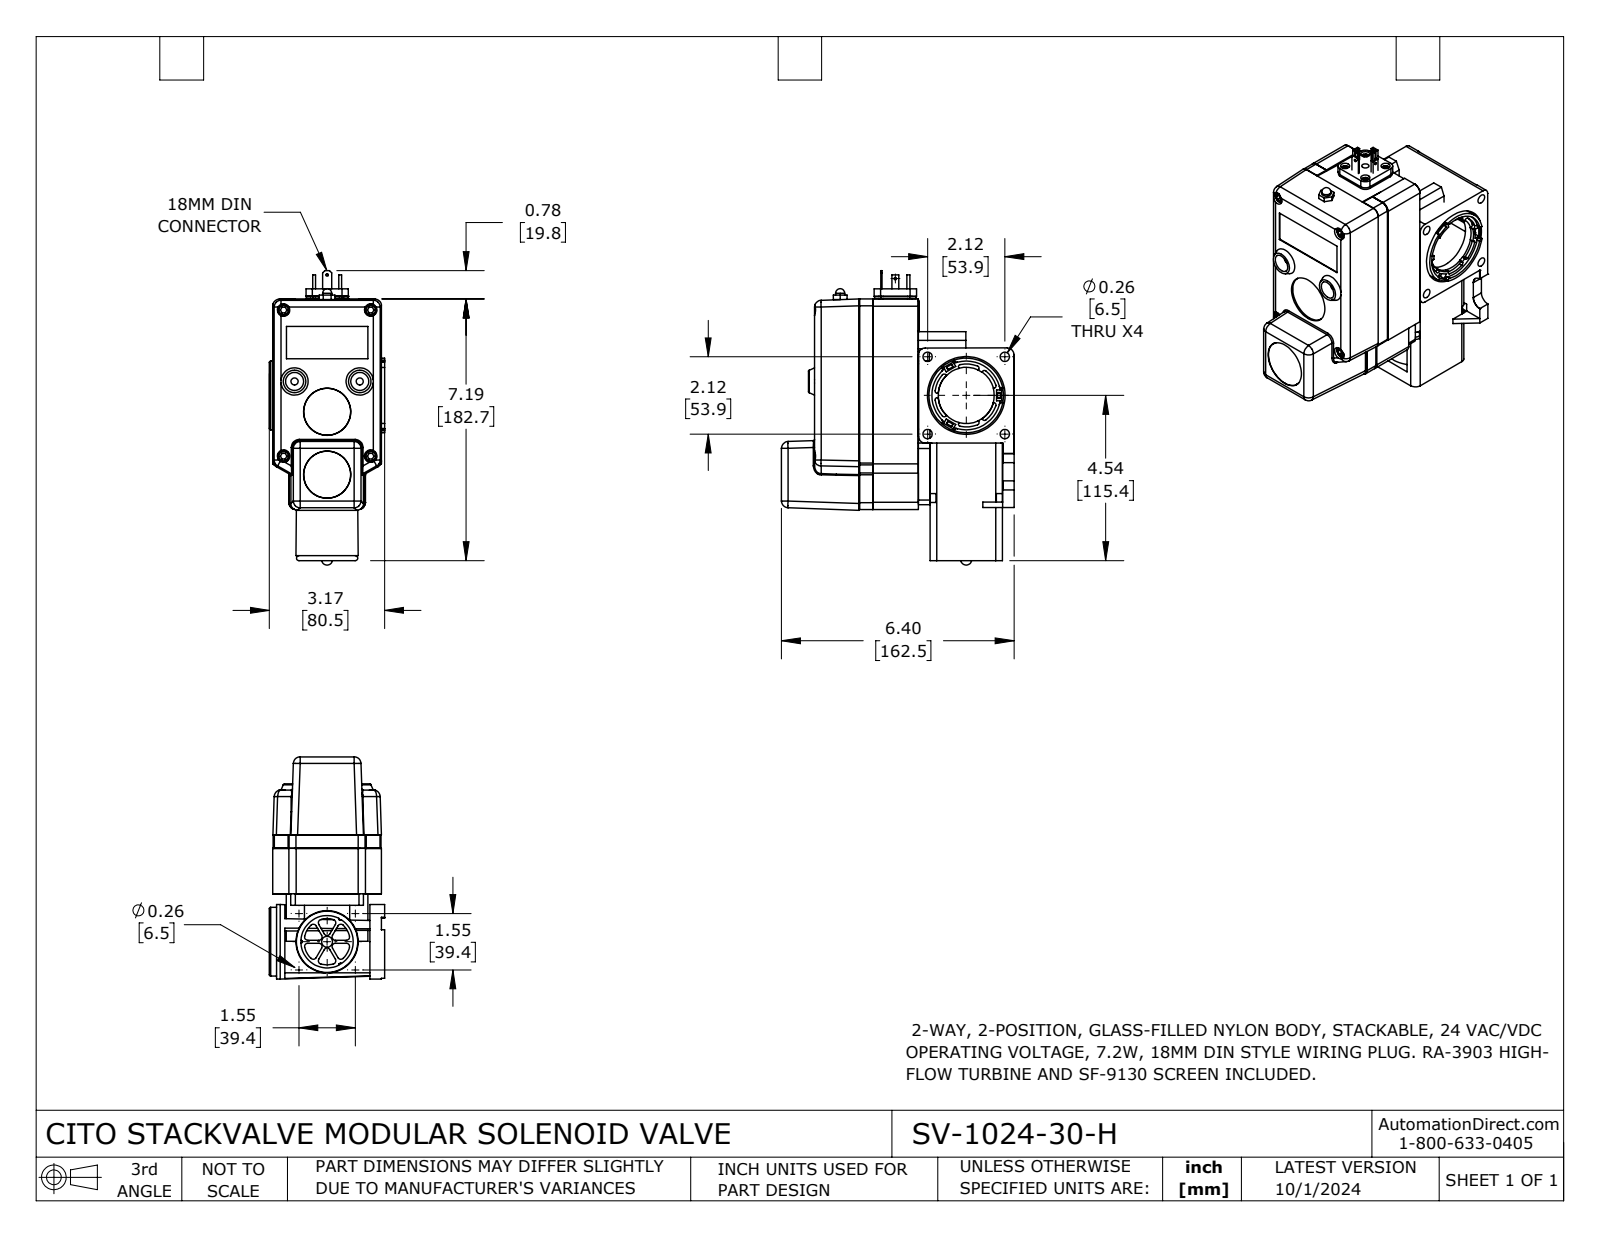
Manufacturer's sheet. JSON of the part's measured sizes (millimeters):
{"part_name": "SV-1024-30-H", "step_written_by": "SolidWorks 2023 (CONFIG_CONTROL_DESIGN)", "units": "millimeters", "bodies": {"solids": 27, "faces": 1281, "planar": 702, "cylindrical": 403, "other": 176}, "overall_size": [205.5, 162.5, 80.5], "volume_mm3": 830700, "surface_area_mm2": 257900, "round_holes": [[3.5, 6], [6.5, 6], [5.5, 4], [6.4, 4], [6.5, 4], [6.5, 4], [8.7, 4], [1.7, 3], [2.4, 3], [5, 2], [9.9, 2], [3.1, 1]], "round_bosses_or_shafts": [[7.9, 5], [4.8, 5], [3.2, 5], [6.2, 3], [32.8, 2], [52.1, 1], [41.9, 1], [36.8, 1]], "partial_cylinders_radius": [[1.6, 18], [2.3, 18], [4.8, 12], [4.4, 8], [1.2, 6], [5.1, 6], [0.8, 5], [4.7, 5]], "face_to_face_distances": [9.5, 63.2, 31.8, 3.8, 58.7, 41.3, 12.7, 108.1, 98.6, 66.9], "hole_center_spacings": [14.1, 20, 38.2, 53.9, 27.8, 39.4, 5.7, 8.6]}
